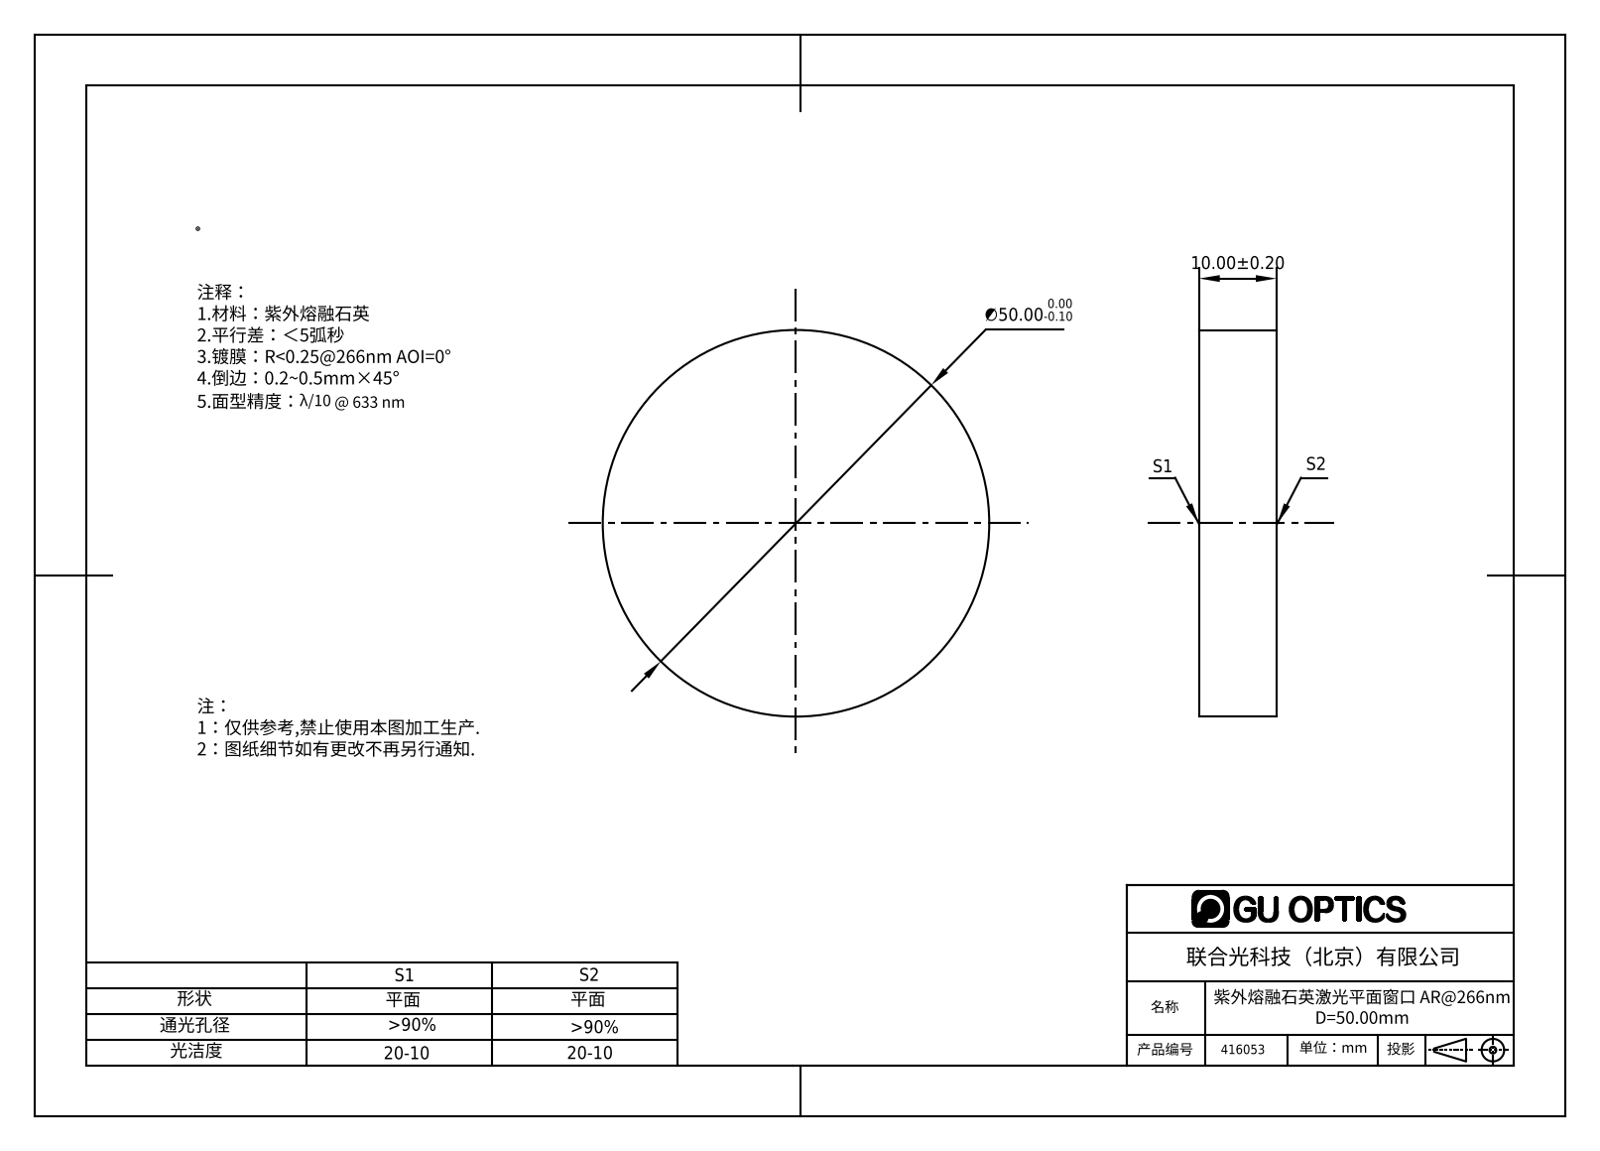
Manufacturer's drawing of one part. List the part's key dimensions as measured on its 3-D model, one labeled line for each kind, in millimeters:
Part name (STEP PRODUCT): 416009
STEP written by: SolidWorks 2016 (CONFIG_CONTROL_DESIGN)
Units: millimetres
Bodies: 1 solid, 4 faces (2 planar, 2 cylindrical, 0 other)
Overall size (bounding box): 50 × 50 × 10
Volume: 19 635 mm³ · Surface area: 5 498 mm²
Round bosses / shafts (diameter × count): ⌀50 ×1
Main face-to-face distances: 10
